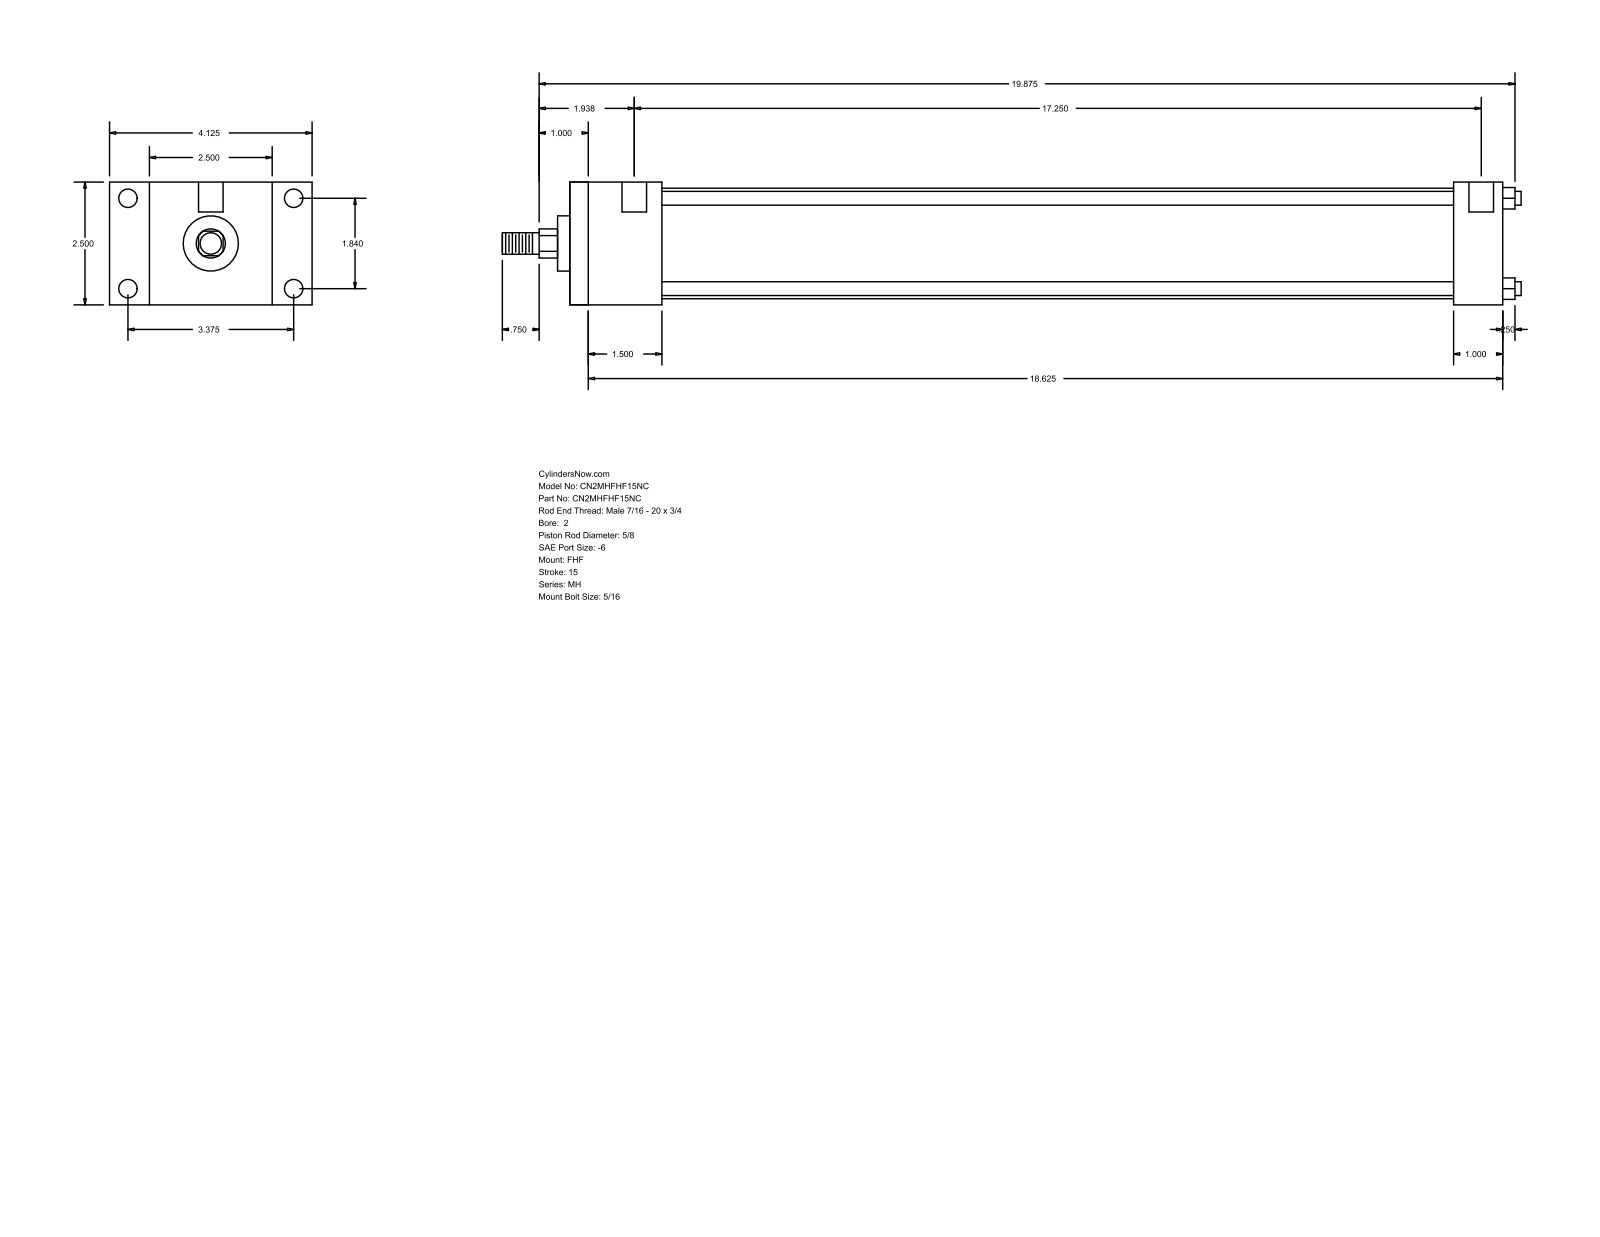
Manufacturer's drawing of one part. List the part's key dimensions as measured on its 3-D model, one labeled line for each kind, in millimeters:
Part name (STEP PRODUCT): MH_FHF__0200_0.625
STEP written by: GSSL Pune (CONFIG_CONTROL_DESIGN)
Units: millimetres
Bodies: 0 solids, 88 faces (60 planar, 28 cylindrical, 0 other)
Overall size (bounding box): 527.05 × 104.78 × 63.5
Round holes (diameter × count): ⌀5.56 ×4, ⌀9.53 ×4, ⌀12.7 ×2
Round bosses / shafts (diameter × count): ⌀7.14 ×4, ⌀57.15 ×1, ⌀28.57 ×1, ⌀15.88 ×1, ⌀11.11 ×1
Partial cylindrical surfaces — rounded edges, fillets, slot ends (radius × count): R7.54 ×1
Main face-to-face distances: 63.5, 47.62, 482.6, 434.98, 20.64, 84.14, 104.78, 457.19, 409.57, 25.41
Hole centre spacings: 46.74, 85.72, 97.63, 446.09, 3.18, 4.76, 438.15, 441.33
